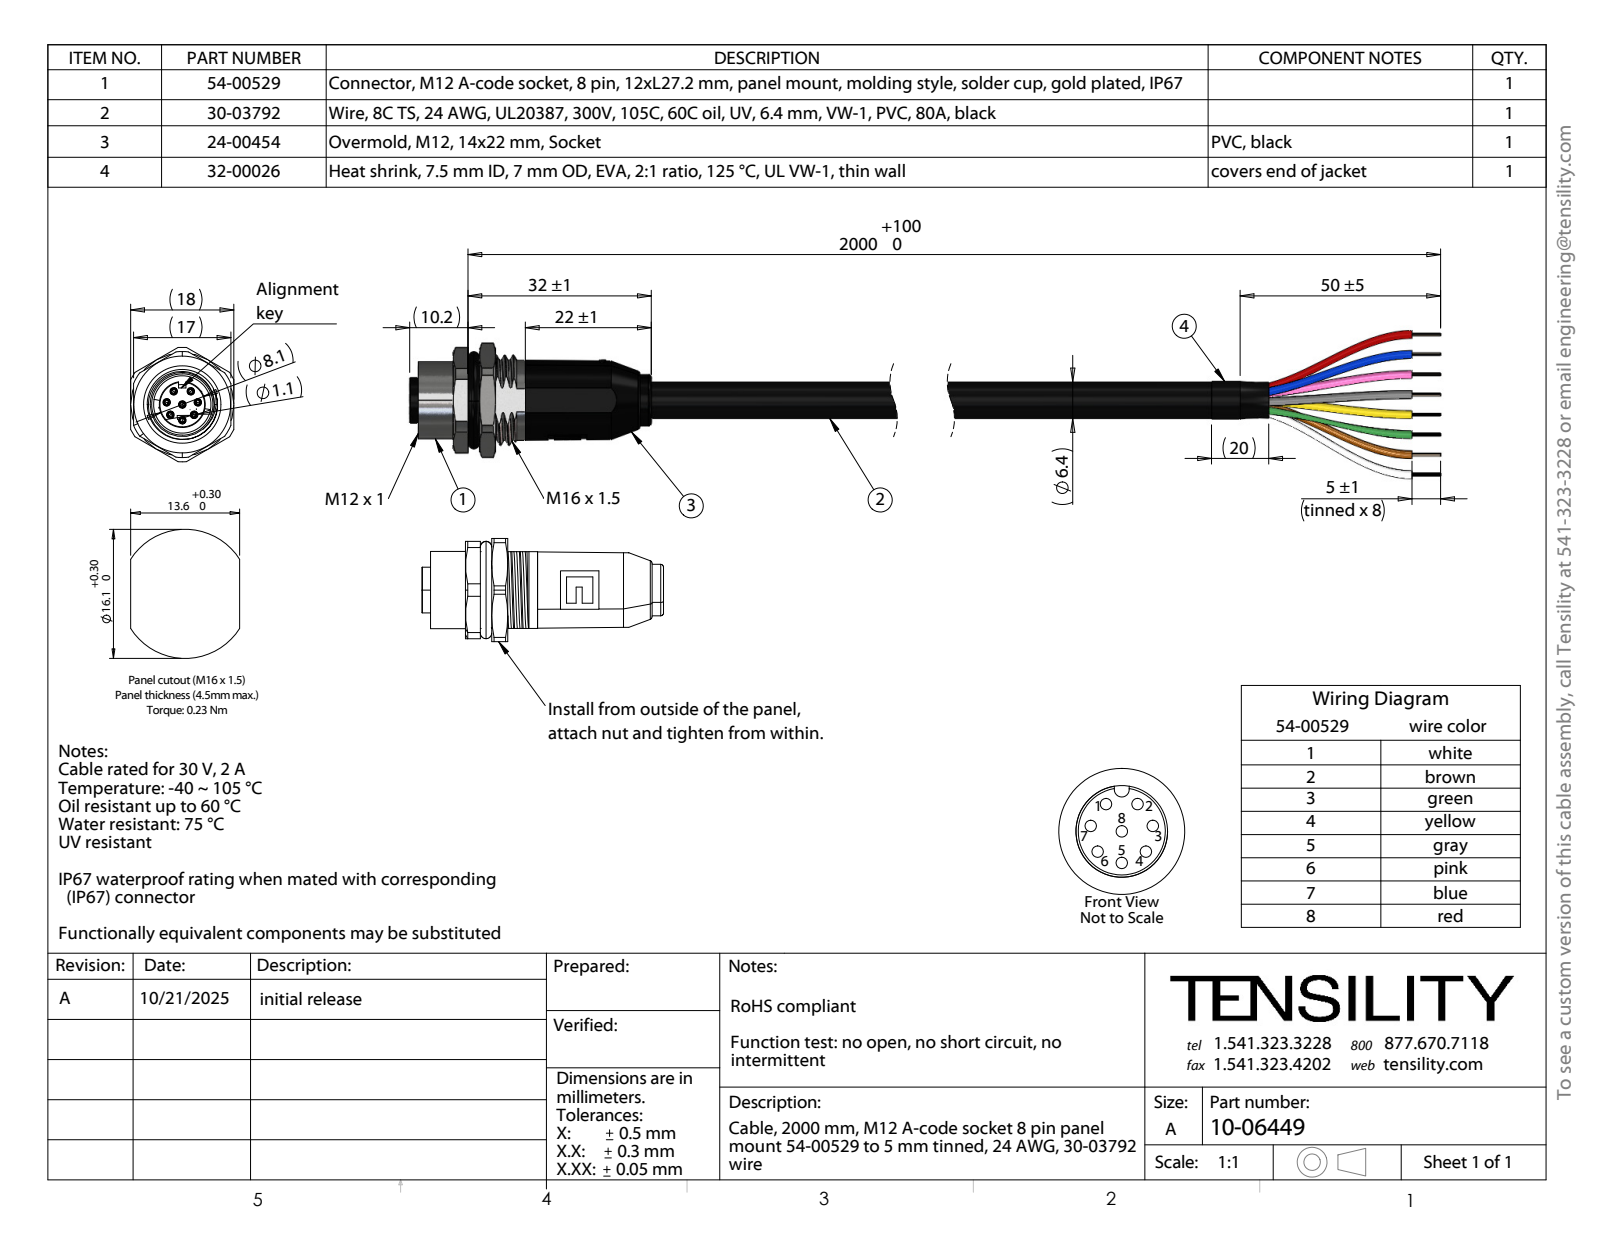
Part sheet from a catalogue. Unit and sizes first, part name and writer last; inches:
Units: inches
Overall size (bounding box): 8.945 × 1.02 × 0.709
Round holes (diameter × count): ⌀0.047 ×8, ⌀0.051 ×8, ⌀0.063 ×8, ⌀0.295 ×1, ⌀0.346 ×1, ⌀0.358 ×1, ⌀0.378 ×1, ⌀0.441 ×1, ⌀0.48 ×1, ⌀0.579 ×1
Round bosses / shafts (diameter × count): ⌀0.067 ×8, ⌀0.061 ×8, ⌀0.06 ×8, ⌀0.549 ×1, ⌀0.531 ×1, ⌀0.492 ×1, ⌀0.433 ×1, ⌀0.421 ×1
Partial cylindrical surfaces — rounded edges, fillets, slot ends (radius × count): R0.02 ×8, R0.277 ×1, R0.311 ×1, R0.364 ×1, R0.394 ×1
Main face-to-face distances: 0.02, 0.079, 0.394, 0.059, 0.102, 0.453, 0.709, 0.374, 0.315, 0.689
Hole centre spacings: 0.108, 0.163, 0.089, 0.09, 0.09, 0.183, 0.207, 0.208
Volume: 0.679 in³ · Surface area: 19.34 in²
Bodies: 336 solids, 2190 faces (893 planar, 967 cylindrical, 330 other)
Part name (STEP PRODUCT): 54-00529; 30-03792_50mm; 32-00026_10 mm; 24-00454 (+2 more)
STEP written by: SolidWorks 2025 (CONFIG_CONTROL_DESIGN)
